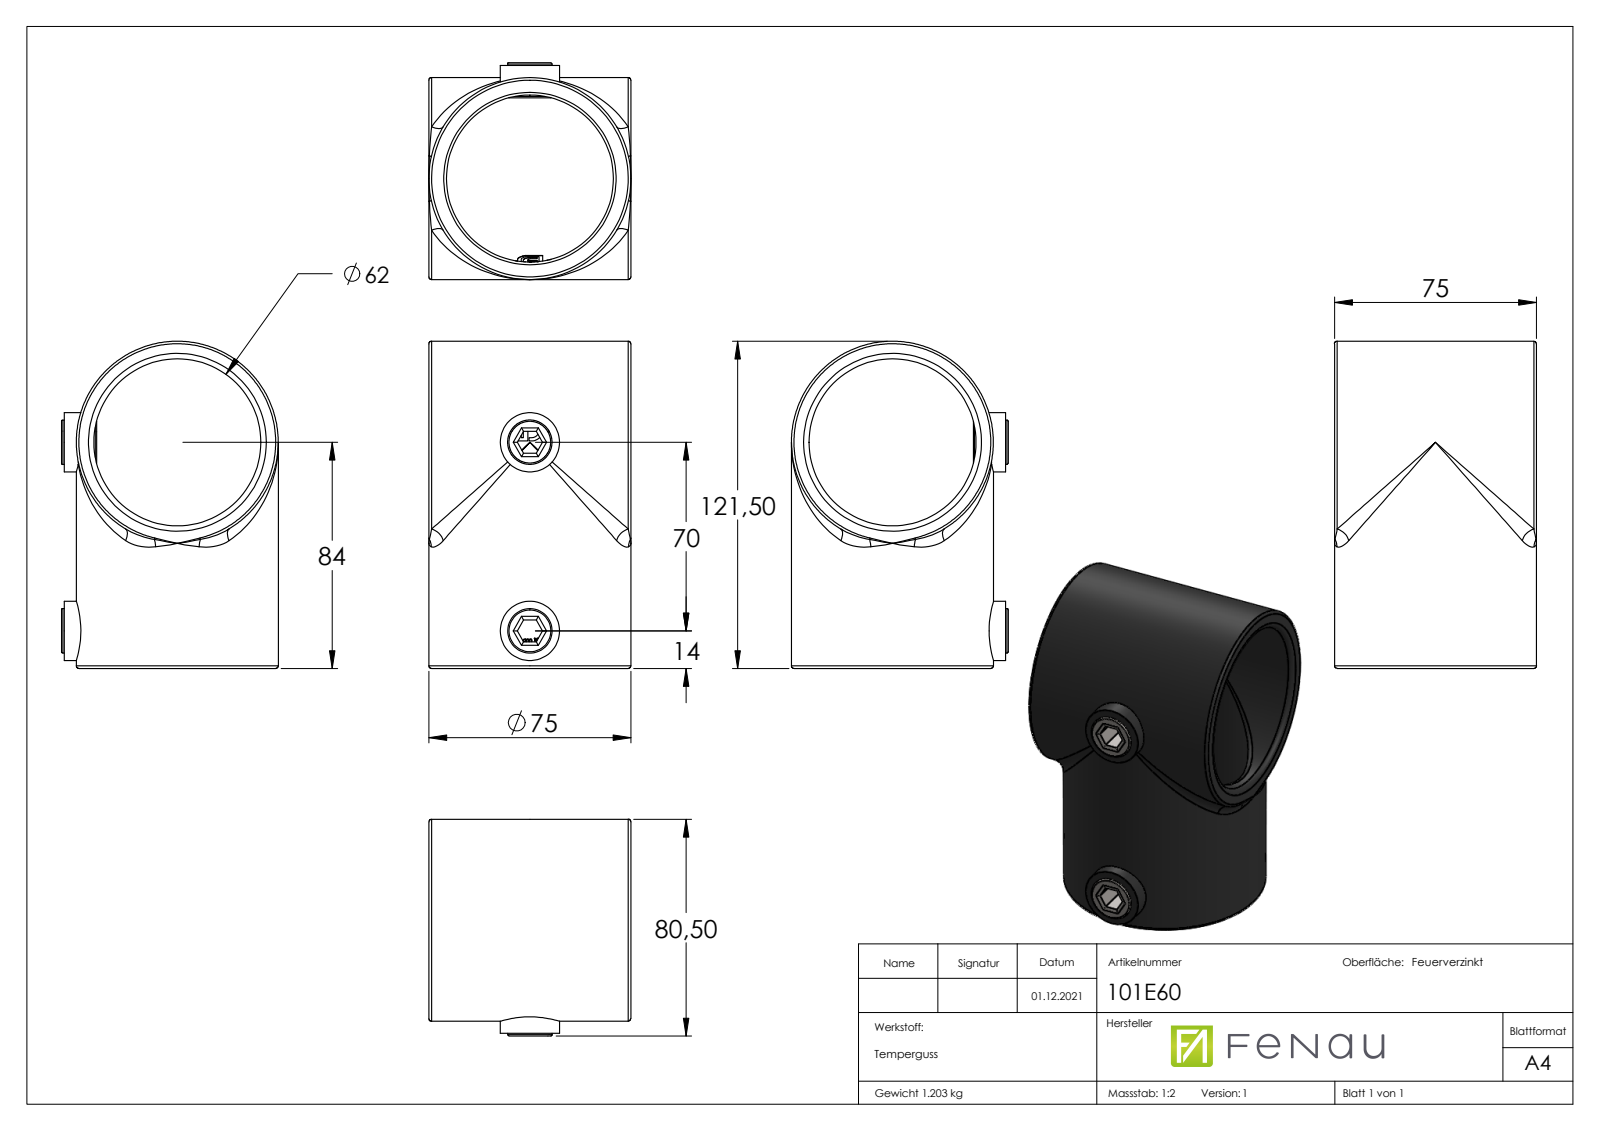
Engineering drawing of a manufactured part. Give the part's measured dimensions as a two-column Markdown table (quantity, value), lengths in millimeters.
| quantity | value |
| --- | --- |
| part name | 101-E60 Teil2; 101-E60 Teil1; 101-E60; 101-E60 Teil1_101-E60 Teil1 |
| STEP written by | SolidWorks 2018 (CONFIG_CONTROL_DESIGN) |
| units | millimeters |
| bodies | 3 solids, 305 faces (126 planar, 56 cylindrical, 123 other) |
| overall size | 121.5 × 80.5 × 75 |
| volume | 164 503 mm³ |
| surface area | 56 525 mm² |
| round holes (diameter × count) | 15.25 × 2, 62 × 2 |
| round bosses / shafts (diameter × count) | 75 × 2, 22 × 2, 16.5 × 2 |
| partial cylindrical surfaces (radius × count) | 2 × 24, 31.1 × 2 |
| main face-to-face distances | 75, 8.1, 35, 1, 12, 13, 43.1, 70, 26.9, 79.95 |
| hole center spacings | 70 |
